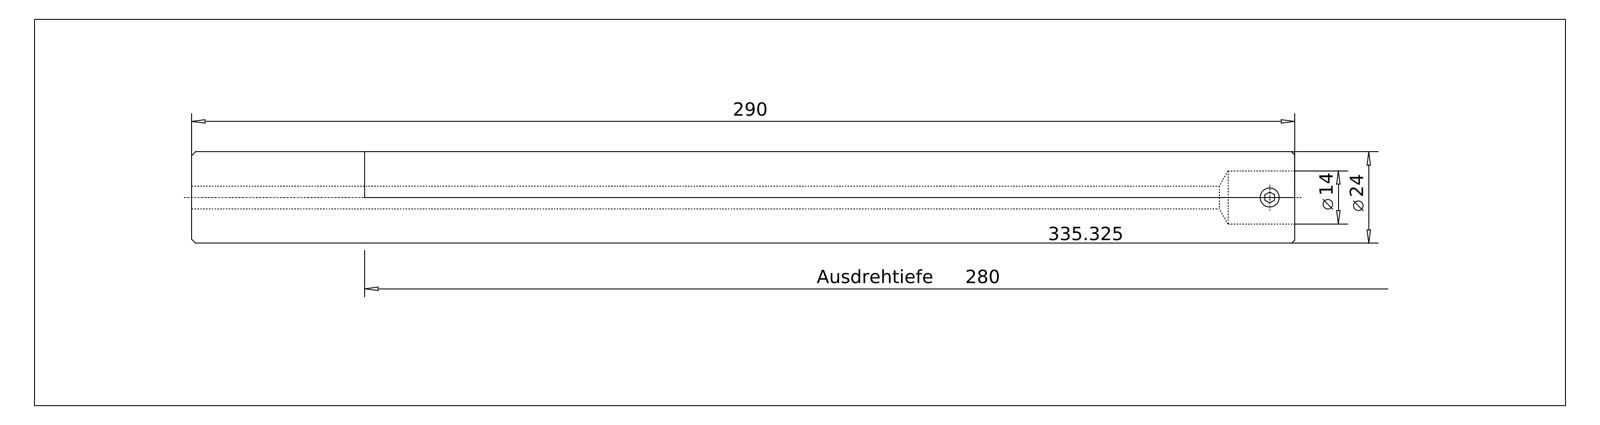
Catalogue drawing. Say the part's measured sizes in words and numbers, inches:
The part is named "335.325 Kaiser D24 X CK2 X 280HM|335.325 Kaiser D24 X CK2 X 280HM_Standard;NONE; 335.325 Kaiser D24 X CK2 X 280HM|690.432 Kaiser ETL M5 X 6,5 CK2_Standard;NONE". Its 3-D file was written by "ACIS (automotive_design)". It is 2 solids with 72 faces: 26 planar, 18 cylindrical and 28 other. Overall it measures 11.024 by 0.945 by 0.945 inches. Its volume is 7.012 cubic inches and its surface area 43.72 square inches. Round holes: 1 of diameter 0.176, 1 of diameter 0.205, 1 of diameter 0.256, 1 of diameter 0.551, 1 of diameter 0.571. Round bosses or shafts: 1 of diameter 0.945, 1 of diameter 0.197. Partial cylindrical surfaces (rounded edges, fillets, slot ends): 2 of radius 0.079. The main face-to-face distances are 11.024, 0.464, 0.272, 10.752, 0.098, 0.256, 0.157.
